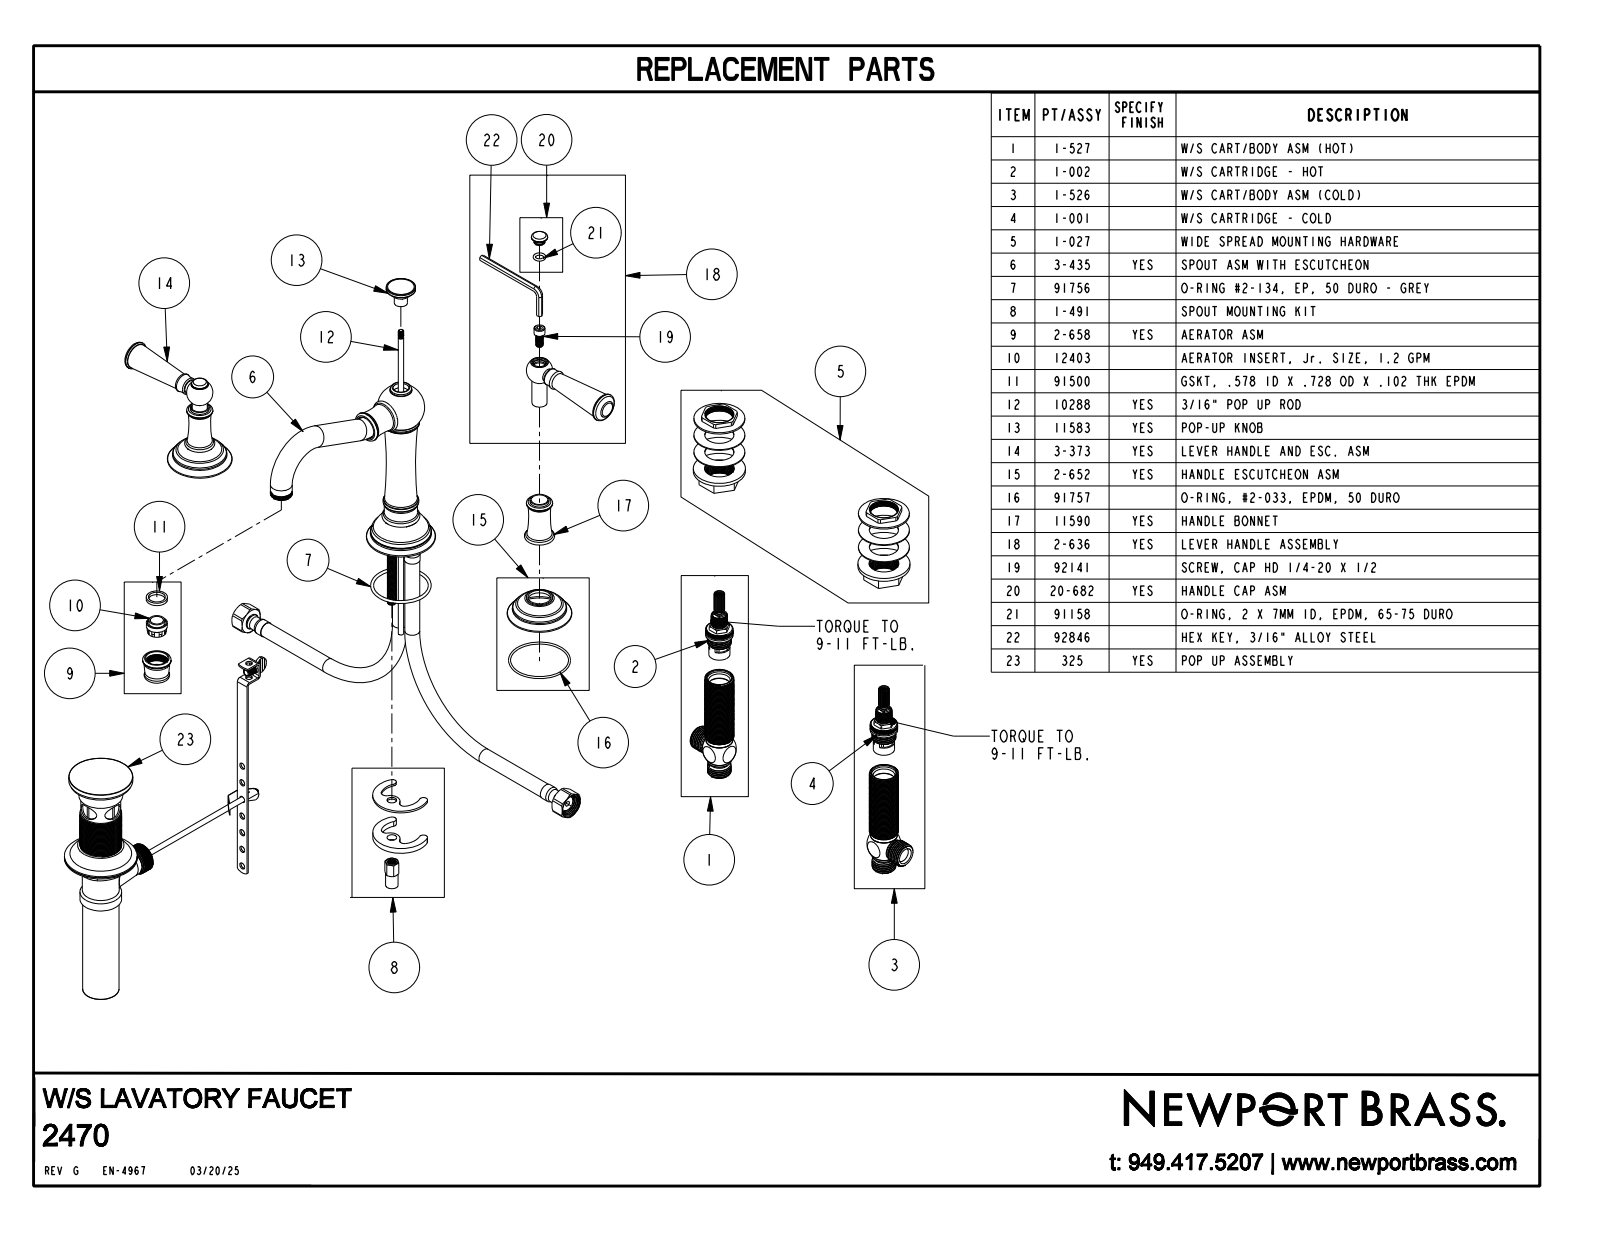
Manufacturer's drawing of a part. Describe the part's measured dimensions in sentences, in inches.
The part is named "2470". Its 3-D file was written by "CREO PARAMETRIC BY PTC INC, 2018400 (CONFIG_CONTROL_DESIGN)". It is 3 solids with 263 faces: 27 planar, 46 cylindrical and 190 other. Overall it measures 14.6 by 7.731 by 6.892 inches. Its volume is 20.27 cubic inches and its surface area 99.99 square inches. Round holes: 1 of diameter 0.543. Round bosses or shafts: 3 of diameter 0.75, 2 of diameter 0.9, 2 of diameter 0.649, 2 of diameter 0.56, 2 of diameter 0.517, 1 of diameter 1.281, 1 of diameter 1.14, 1 of diameter 1.05. The main face-to-face distances are 4.201, 2.14, 2.061, 2.22, 0.08, 1.981, 14.6, 1.05, 4.971, 2.831.
